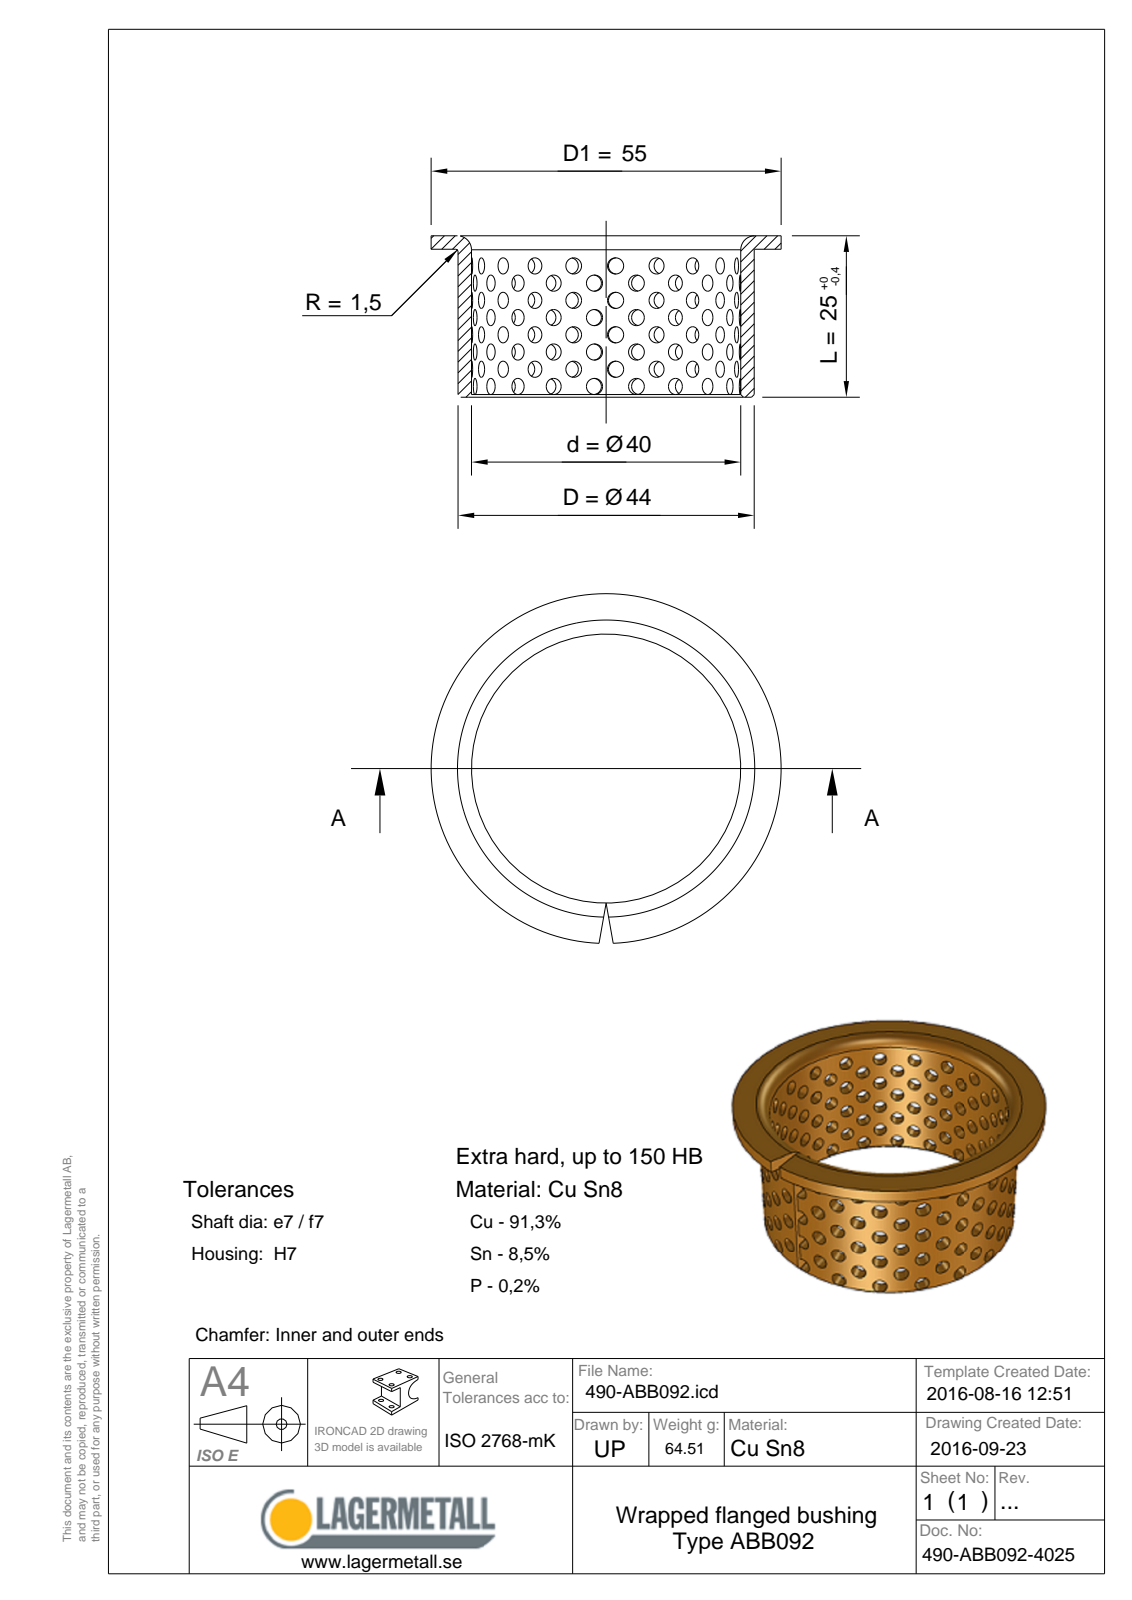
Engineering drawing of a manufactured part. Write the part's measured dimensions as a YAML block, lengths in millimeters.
step_written_by: "Spatial InterOp 3D (CONFIG_CONTROL_DESIGN)"
units: millimeters
bodies: {solids: 1, faces: 25, planar: 5, cylindrical: 8, other: 12}
overall_size: [55, 55, 25]
volume: 7964
surface_area: 8634
round_holes:
  - {diameter: 40, count: 1}
round_bosses_or_shafts:
  - {diameter: 55, count: 1}
  - {diameter: 44, count: 1}
face_to_face_distances: [2, 23, 25]
